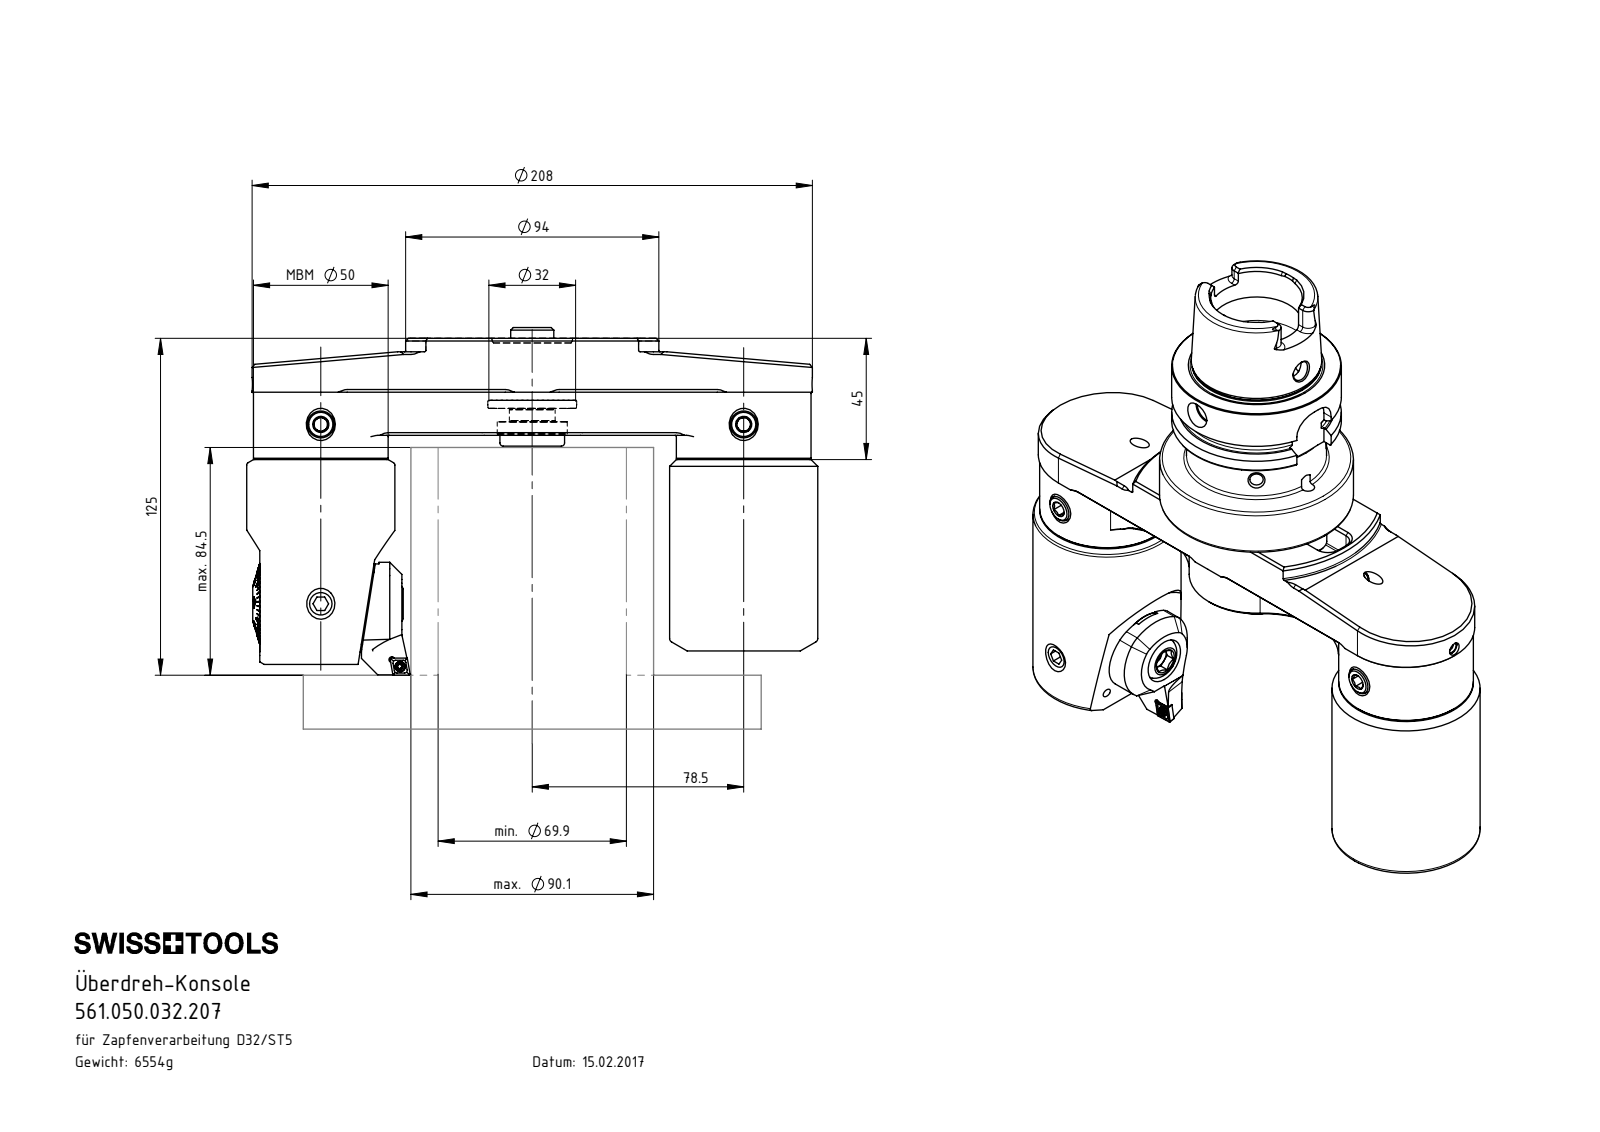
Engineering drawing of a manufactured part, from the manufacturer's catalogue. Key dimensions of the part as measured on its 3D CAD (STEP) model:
Part name (STEP PRODUCT): CWF-ST5.Ko1.071_A; KoU.D32.ST5.207; KVT_MB_600_050; DIN 7984 - M16 x 35 (+2 more)
STEP written by: SolidWorks 2017 (AUTOMOTIVE_DESIGN)
Units: millimetres
Bodies: 13 solids, 368 faces (123 planar, 81 cylindrical, 164 other)
Overall size (bounding box): 210 × 120 × 55
Volume: 424 888 mm³ · Surface area: 76 040 mm²
Round holes (diameter × count): ⌀4 ×5, ⌀4.2 ×5, ⌀5 ×2, ⌀9 ×2, ⌀28 ×2, ⌀30 ×2, ⌀2 ×1, ⌀6.8 ×1, ⌀10.2 ×1, ⌀17 ×1, ⌀26 ×1, ⌀32 ×1
Round bosses / shafts (diameter × count): ⌀5 ×3, ⌀50 ×2, ⌀10 ×2, ⌀55 ×1, ⌀27.8 ×1, ⌀27.3 ×1, ⌀24 ×1, ⌀16 ×1
Partial cylindrical surfaces — rounded edges, fillets, slot ends (radius × count): R0.5 ×4, R4.2 ×4, R4.5 ×4, R27.77 ×4, R25.5 ×2, R25 ×1, R47 ×1
Main face-to-face distances: 5, 16, 25, 20, 9, 45, 51, 10, 36, 26
Hole centre spacings: 157, 16.9, 78.5, 0.5, 33.8, 61.6, 95.4, 140.1
